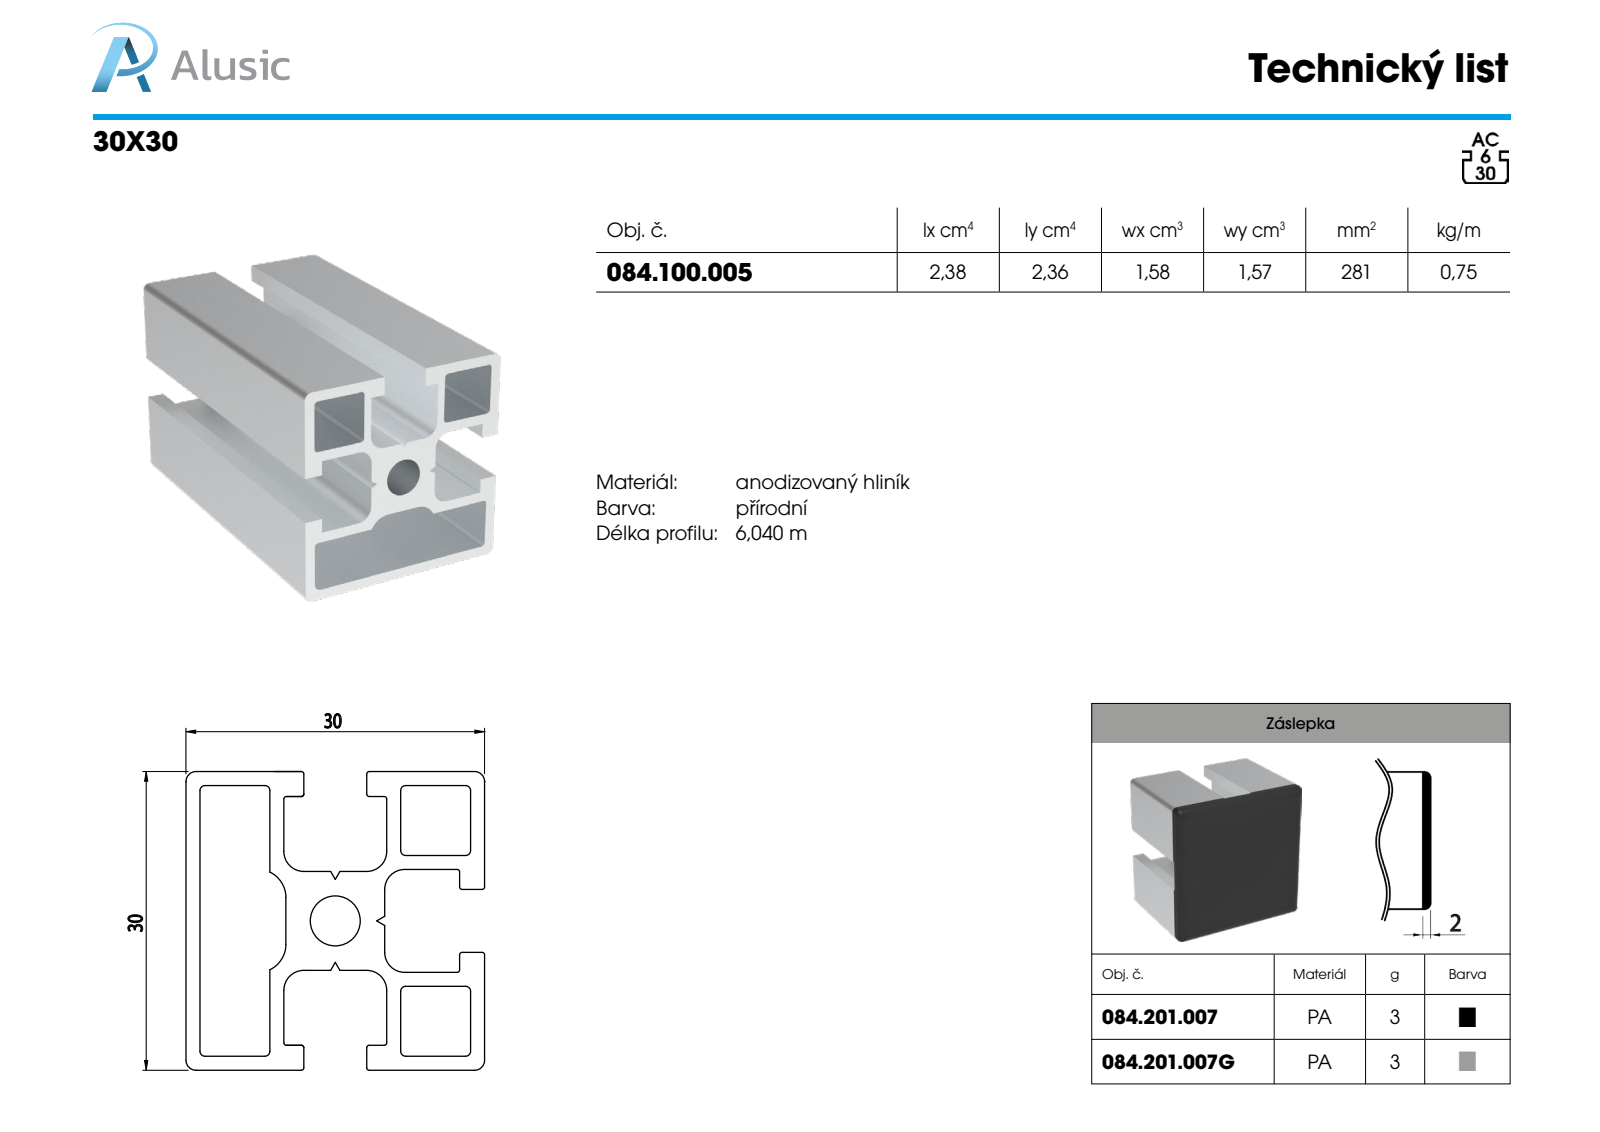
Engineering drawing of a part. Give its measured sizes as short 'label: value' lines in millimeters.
name: 084.100.005
written by: SolidWorks 2011 (CONFIG_CONTROL_DESIGN)
unit: mm
bodies: 1 solid, 79 faces (53 planar, 26 cylindrical, 0 other)
size: 100 × 30 × 30
volume: 29 440 mm³; area: 34 701 mm²
holes: 1× ⌀5.15
rounds: 11× R0.5, 6× R2, 5× R1, 2× R2.8
face distances: 1.4, 8.45, 20.15, 28.6, 30, 9.85, 18.75, 21.55, 7.05, 27.2
